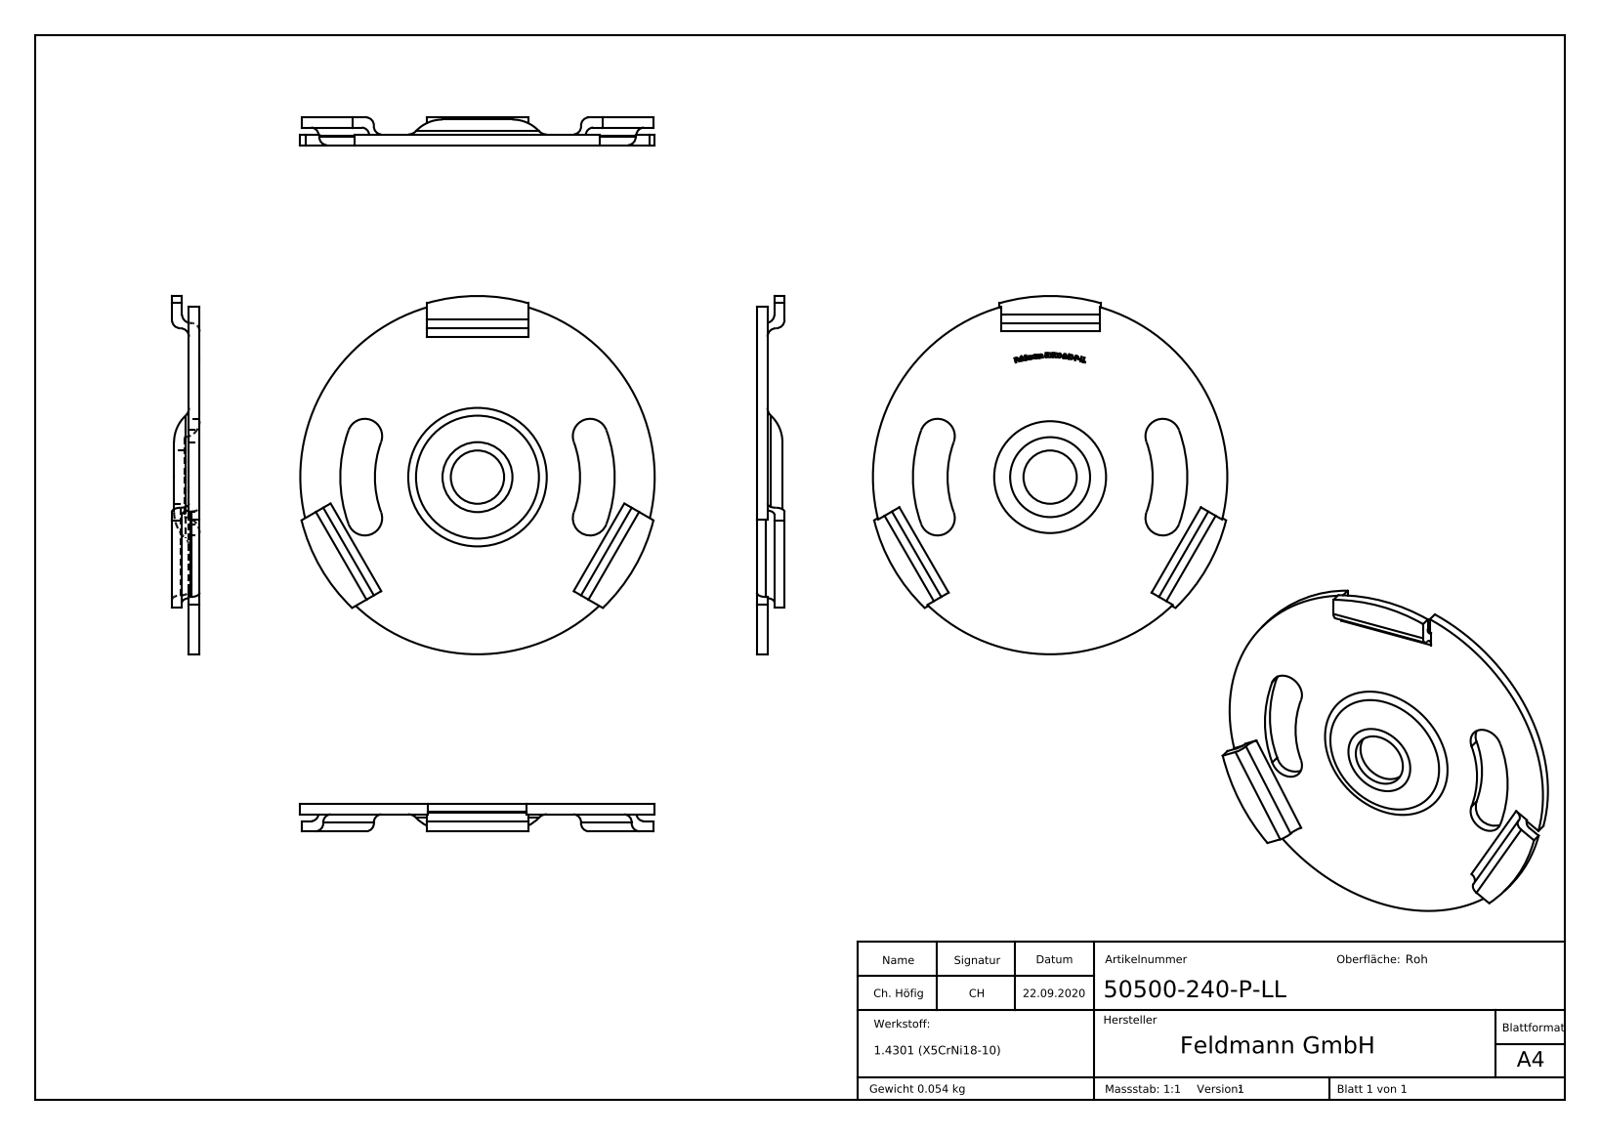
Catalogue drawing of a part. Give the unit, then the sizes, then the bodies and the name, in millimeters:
Units: millimetres
Overall size (bounding box): 67.25 × 66.5 × 5.2
Round holes (diameter × count): ⌀10 ×1
Partial cylindrical surfaces — rounded edges, fillets, slot ends (radius × count): R1.6 ×12, R3.25 ×4, R19.25 ×1, R25.75 ×1, R33.25 ×1, R34 ×1
Main face-to-face distances: 2, 3.2, 1.9, 5.2, 3.3, 1.3, 0.4, 2.9, 0.9, 2.3
Volume: 6 873 mm³ · Surface area: 7 482 mm²
Bodies: 1 solid, 324 faces (173 planar, 33 cylindrical, 118 other)
Part name (STEP PRODUCT): 50500-240-P-LL
STEP written by: SolidWorks 2018 (CONFIG_CONTROL_DESIGN)
